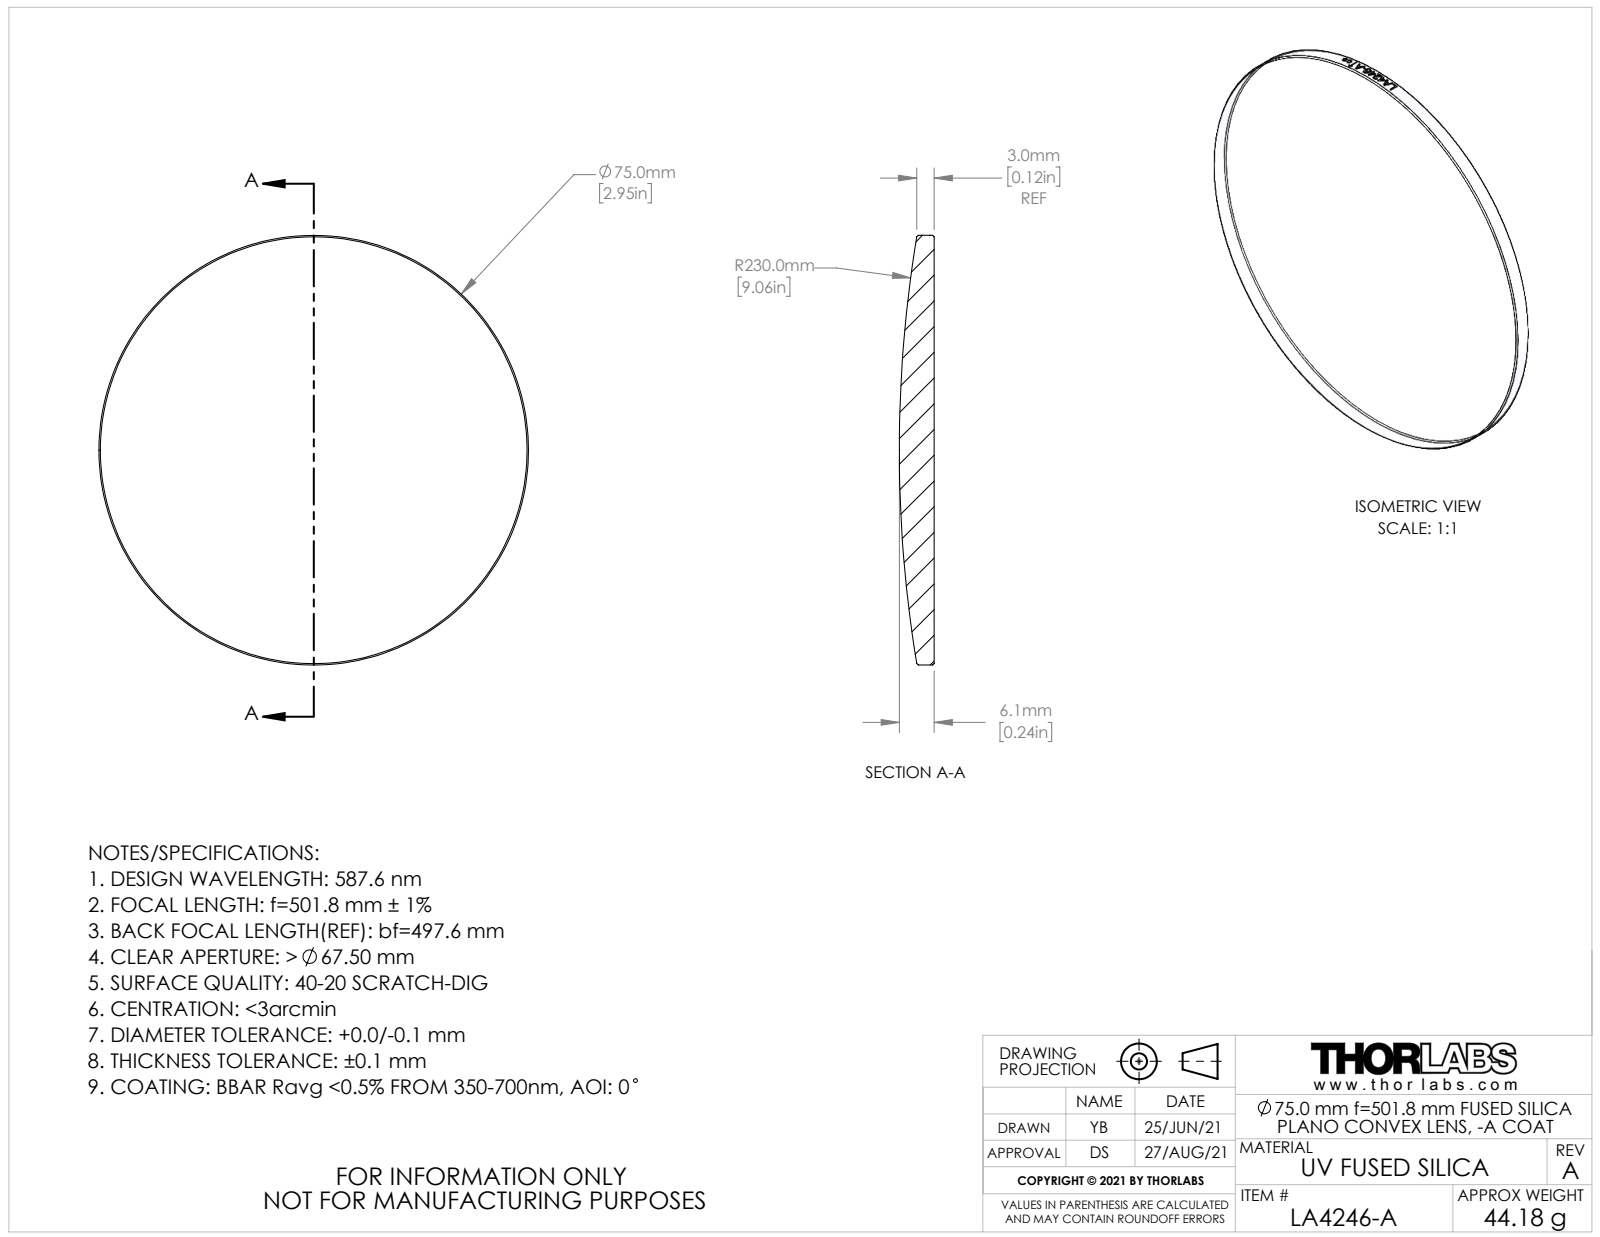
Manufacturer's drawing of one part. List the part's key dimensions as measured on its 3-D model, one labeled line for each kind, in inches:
Part name (STEP PRODUCT): CTN017548-E0W; CTN017576
STEP written by: SolidWorks 2018 (AUTOMOTIVE_DESIGN)
Units: inches
Bodies: 1 solid, 26 faces (1 planar, 19 cylindrical, 6 other)
Overall size (bounding box): 2.953 × 2.953 × 0.239
Volume: 1.224 in³ · Surface area: 14.74 in²
Round bosses / shafts (diameter × count): ⌀2.953 ×1
